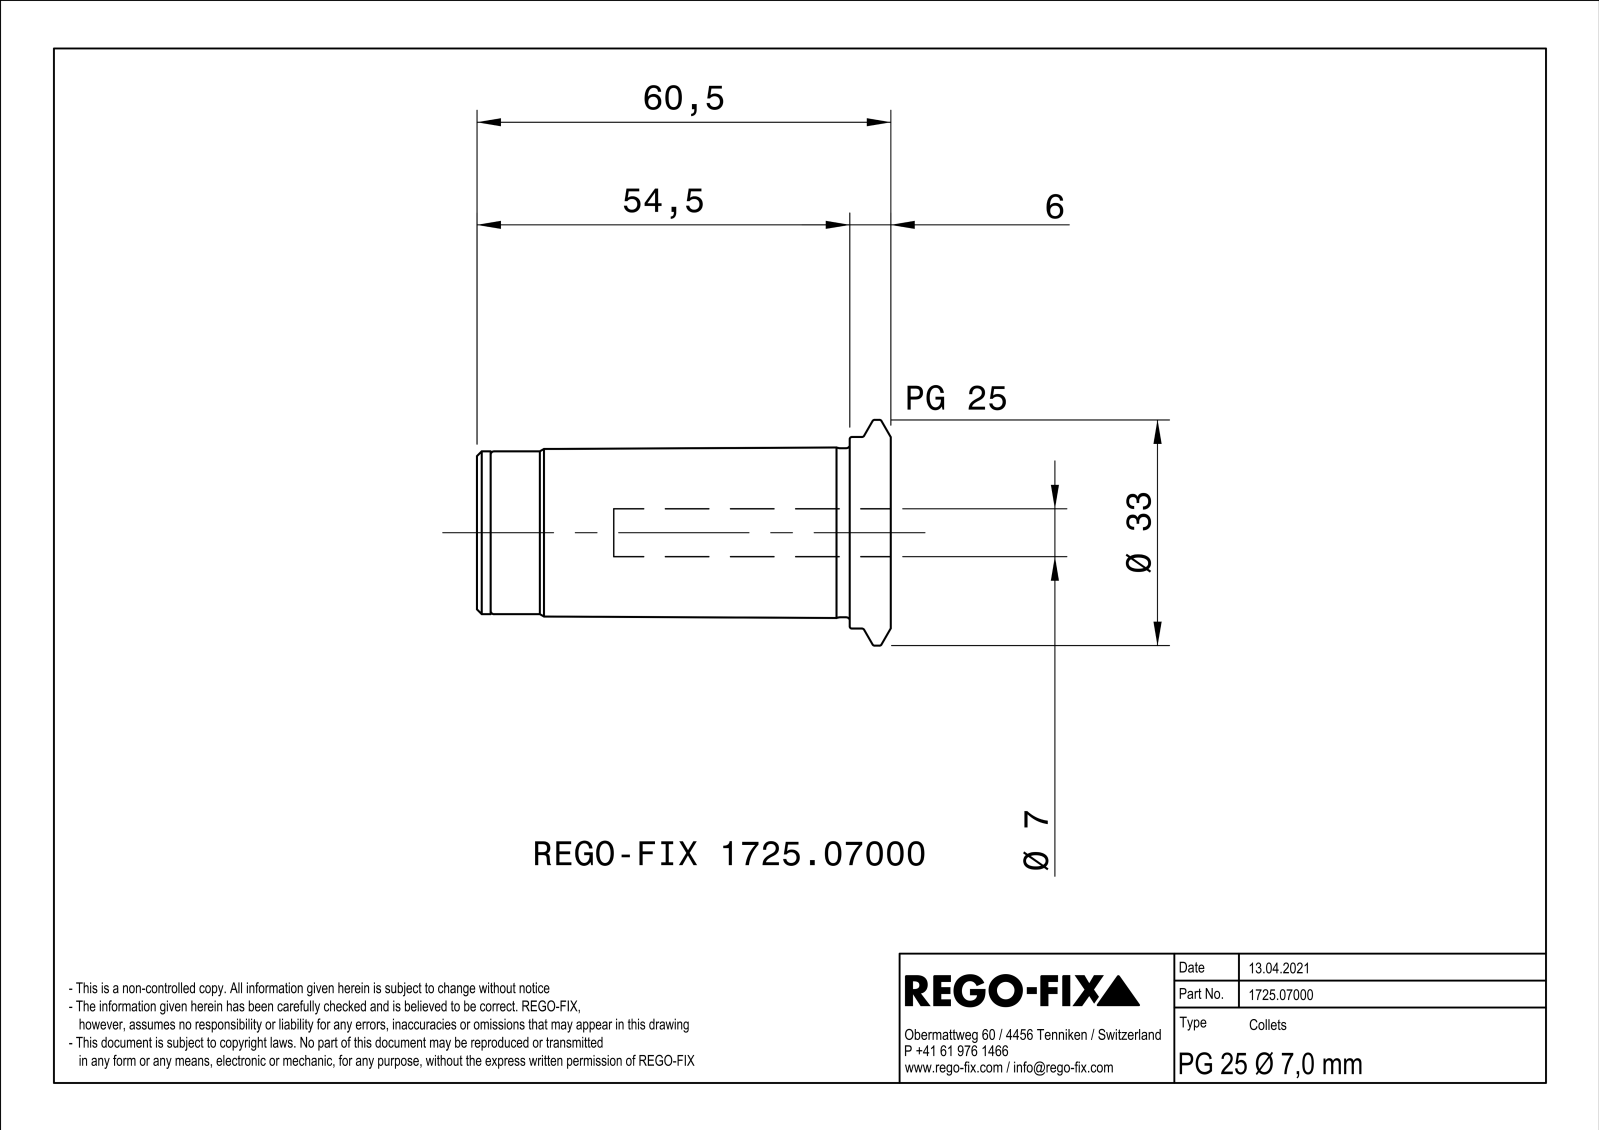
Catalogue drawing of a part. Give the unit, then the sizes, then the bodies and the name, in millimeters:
Units: millimetres
Overall size (bounding box): 60.5 × 33 × 32.99
Round holes (diameter × count): ⌀2.5 ×3, ⌀5.2 ×1, ⌀6.92 ×1, ⌀7 ×1, ⌀8.2 ×1, ⌀9 ×1, ⌀20.4 ×1, ⌀20.92 ×1, ⌀22.2 ×1
Round bosses / shafts (diameter × count): ⌀33 ×1, ⌀28 ×1, ⌀24.7 ×1, ⌀23.8 ×1, ⌀12 ×1
Main face-to-face distances: 1, 60.5, 52.6, 7.9, 58.5, 5.9, 2, 50, 2.6, 8.5
Hole centre spacings: 7.75, 13.43, 13.42
Bodies: 1 solid, 87 faces (23 planar, 24 cylindrical, 40 other)
Part name (STEP PRODUCT): NOCUT
STEP written by: SIEMENS PLM Software Solid Edge ST10 (AUTOMOTIVE_DESIGN)
